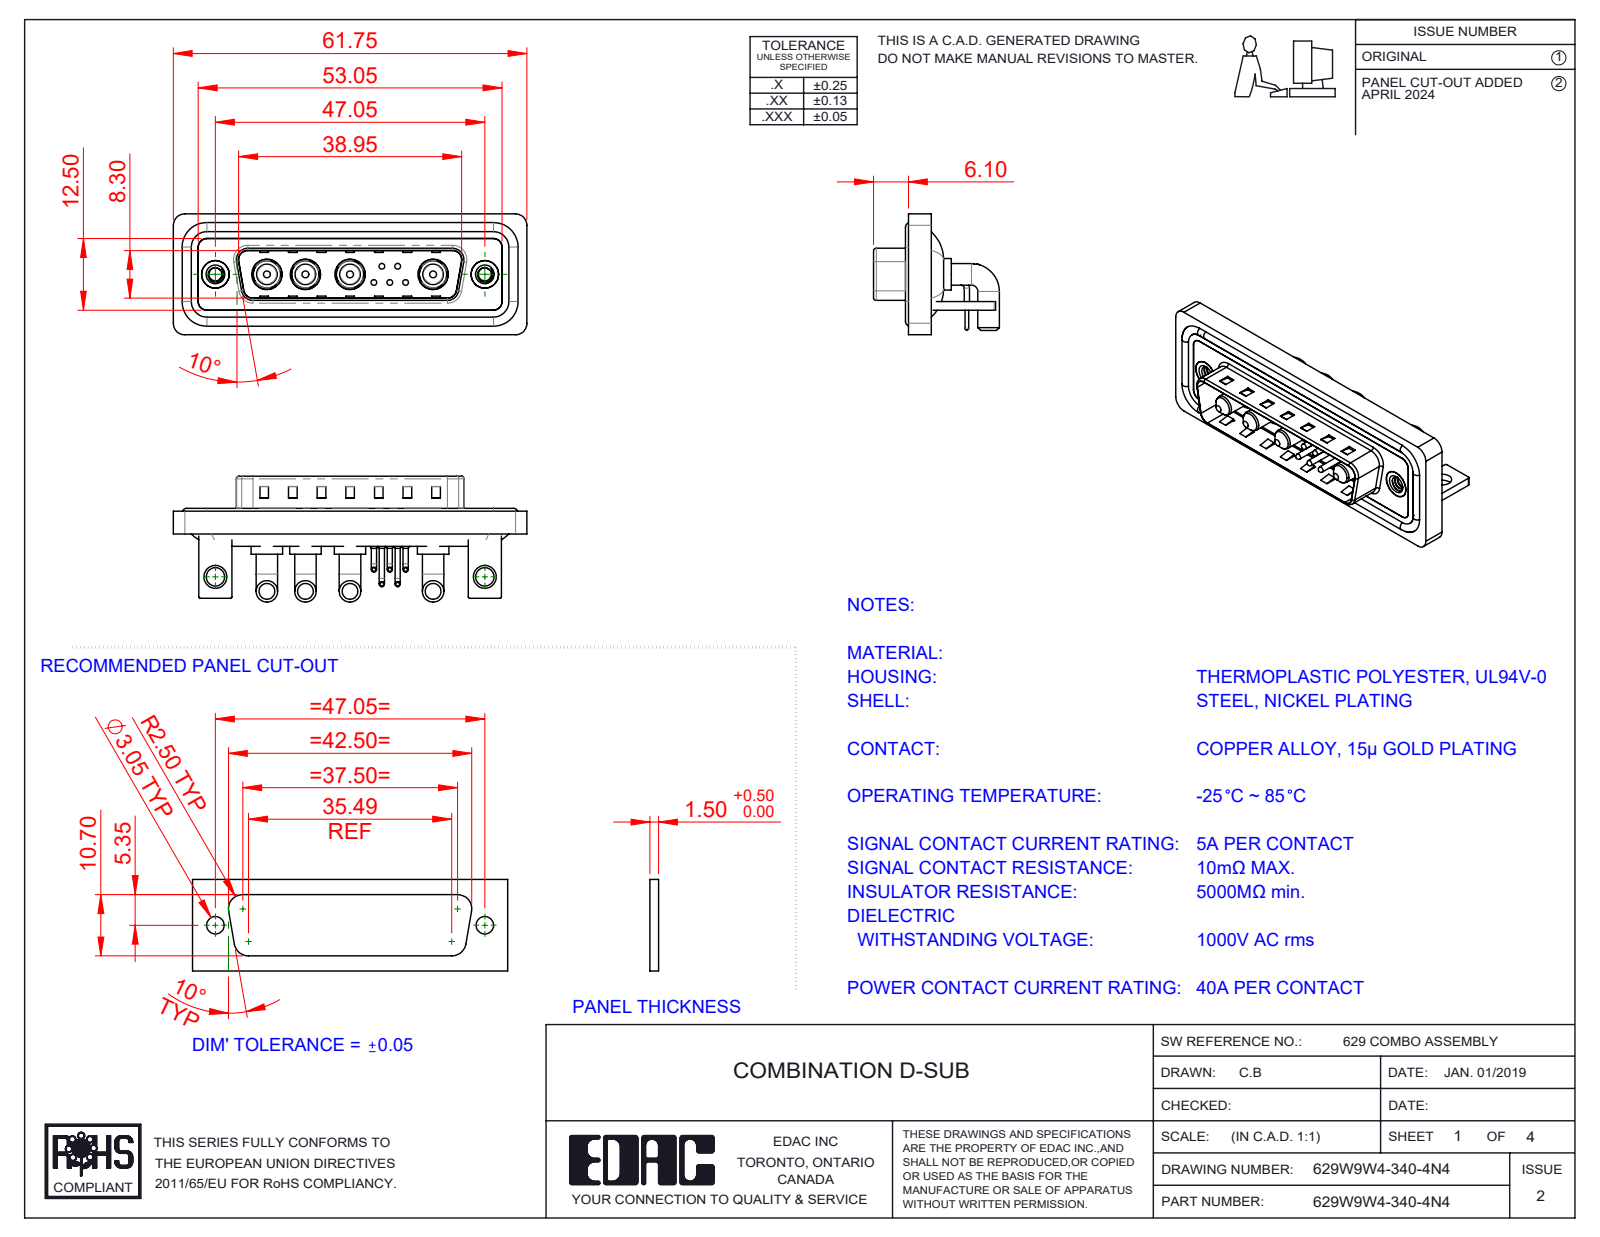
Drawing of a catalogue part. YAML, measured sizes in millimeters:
part_name: "629Combo Contact Row 2; 629Combo Stabilizer Bracket; 629Combo Housing_9W4; 629Combo Shell Rear_25 Contacts (+6 more)"
step_written_by: "SolidWorks 2023 (CONFIG_CONTROL_DESIGN)"
units: millimeters
bodies: {solids: 22, faces: 1245, planar: 589, cylindrical: 470, other: 186}
overall_size: [61.75, 21.98, 21.1]
volume: 8274
surface_area: 13139
round_holes:
  - {diameter: 0.75, count: 5}
  - {diameter: 1.6, count: 5}
  - {diameter: 2, count: 5}
  - {diameter: 4.85, count: 4}
  - {diameter: 5.3, count: 4}
  - {diameter: 2.26, count: 2}
  - {diameter: 3.2, count: 2}
  - {diameter: 4, count: 2}
  - {diameter: 4.8, count: 2}
  - {diameter: 5, count: 2}
round_bosses_or_shafts:
  - {diameter: 0.9, count: 10}
  - {diameter: 3.75, count: 8}
  - {diameter: 1.5, count: 5}
  - {diameter: 1, count: 5}
  - {diameter: 0.65, count: 5}
  - {diameter: 5.5, count: 4}
  - {diameter: 5.2, count: 4}
  - {diameter: 4.75, count: 4}
partial_cylinders:
  - {radius: 2, count: 19}
  - {radius: 1.5, count: 18}
  - {radius: 0.25, count: 16}
  - {radius: 0.5, count: 9}
  - {radius: 1.6, count: 8}
  - {radius: 1.01, count: 5}
  - {radius: 0.6, count: 4}
  - {radius: 0.65, count: 4}
face_to_face_distances: [0.4, 1.5, 0.8, 2.9, 2.1, 1.1, 3.7, 4.1, 4.5, 1.6]
hole_center_spacings: [3.16, 2.77, 5.04, 14.5, 47.05, 2.78, 4.4, 4.41]
